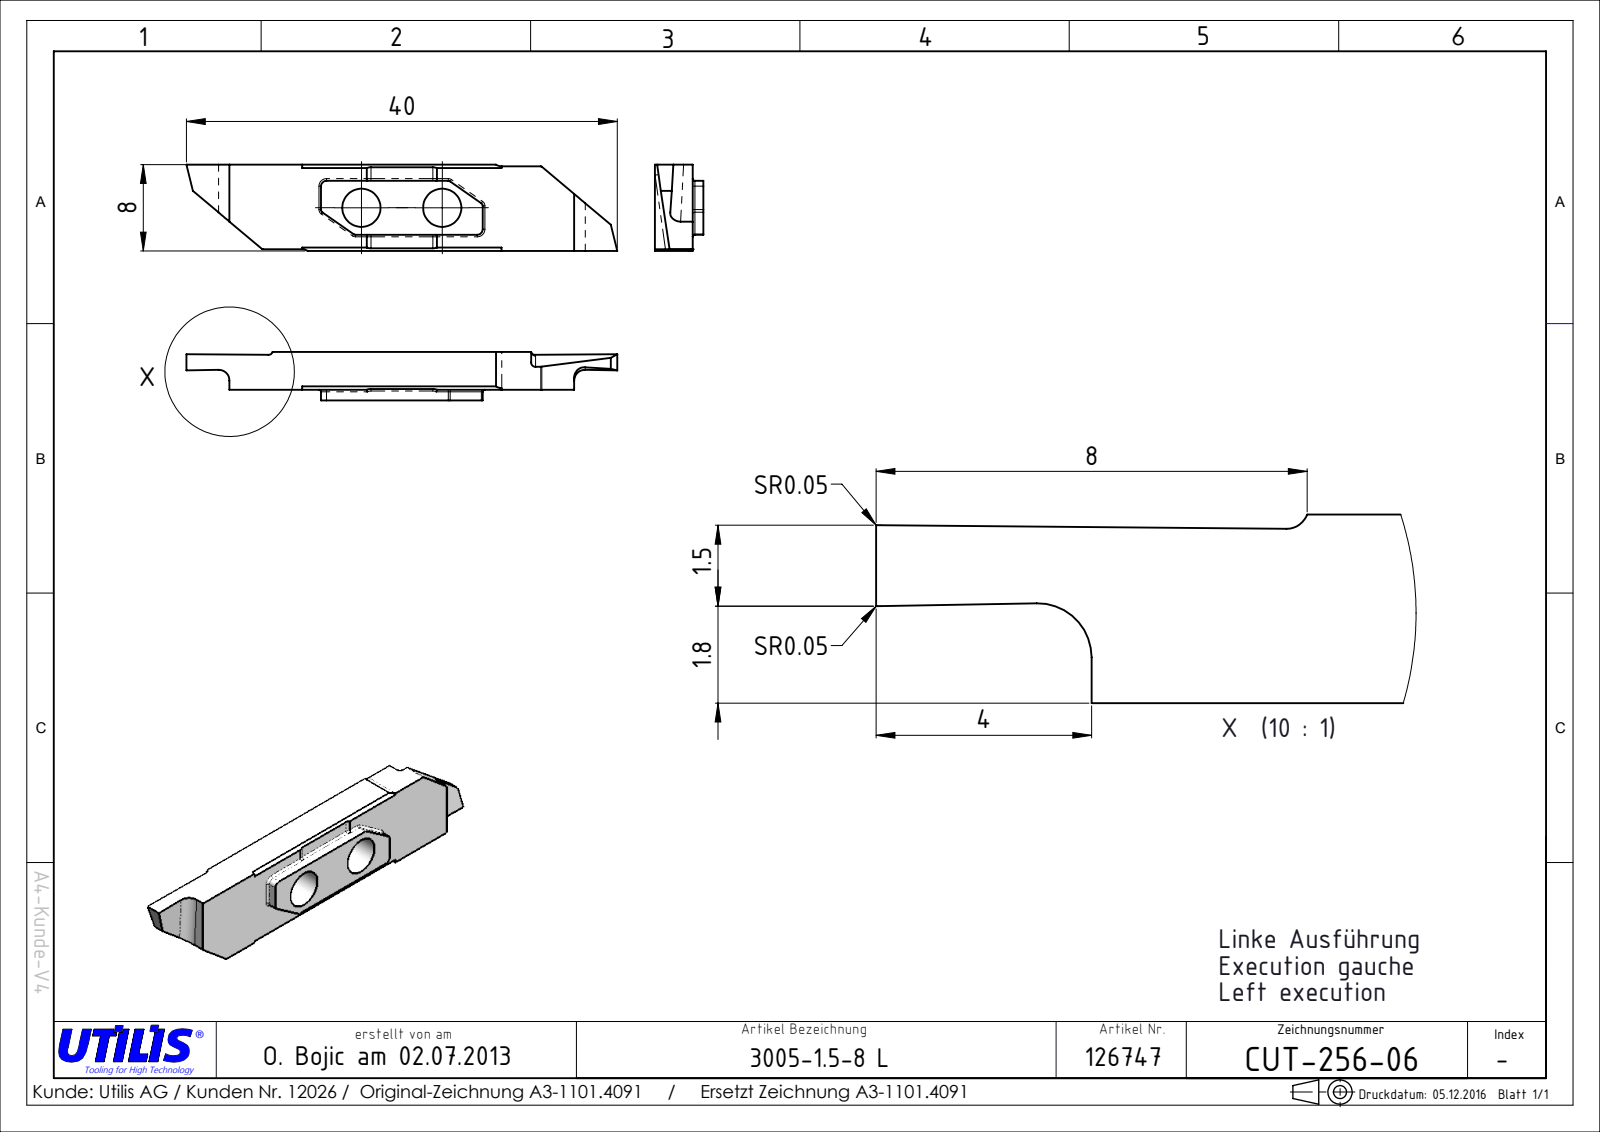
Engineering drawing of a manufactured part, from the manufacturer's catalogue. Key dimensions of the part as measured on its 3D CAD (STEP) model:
Part name (STEP PRODUCT): CUT-256-06
STEP written by: SolidWorks 2016 (AUTOMOTIVE_DESIGN)
Units: millimetres
Bodies: 1 solid, 38 faces (24 planar, 14 cylindrical, 0 other)
Overall size (bounding box): 40 × 8 × 3.5
Volume: 820 mm³ · Surface area: 858 mm²
Round holes (diameter × count): ⌀3.55 ×2
Partial cylindrical surfaces — rounded edges, fillets, slot ends (radius × count): R0.15 ×4, R1 ×4, R0.4 ×2
Main face-to-face distances: 3.5, 8, 7.85, 22.54, 7.7, 4, 36, 32, 40, 38.98
Hole centre spacings: 7.5
